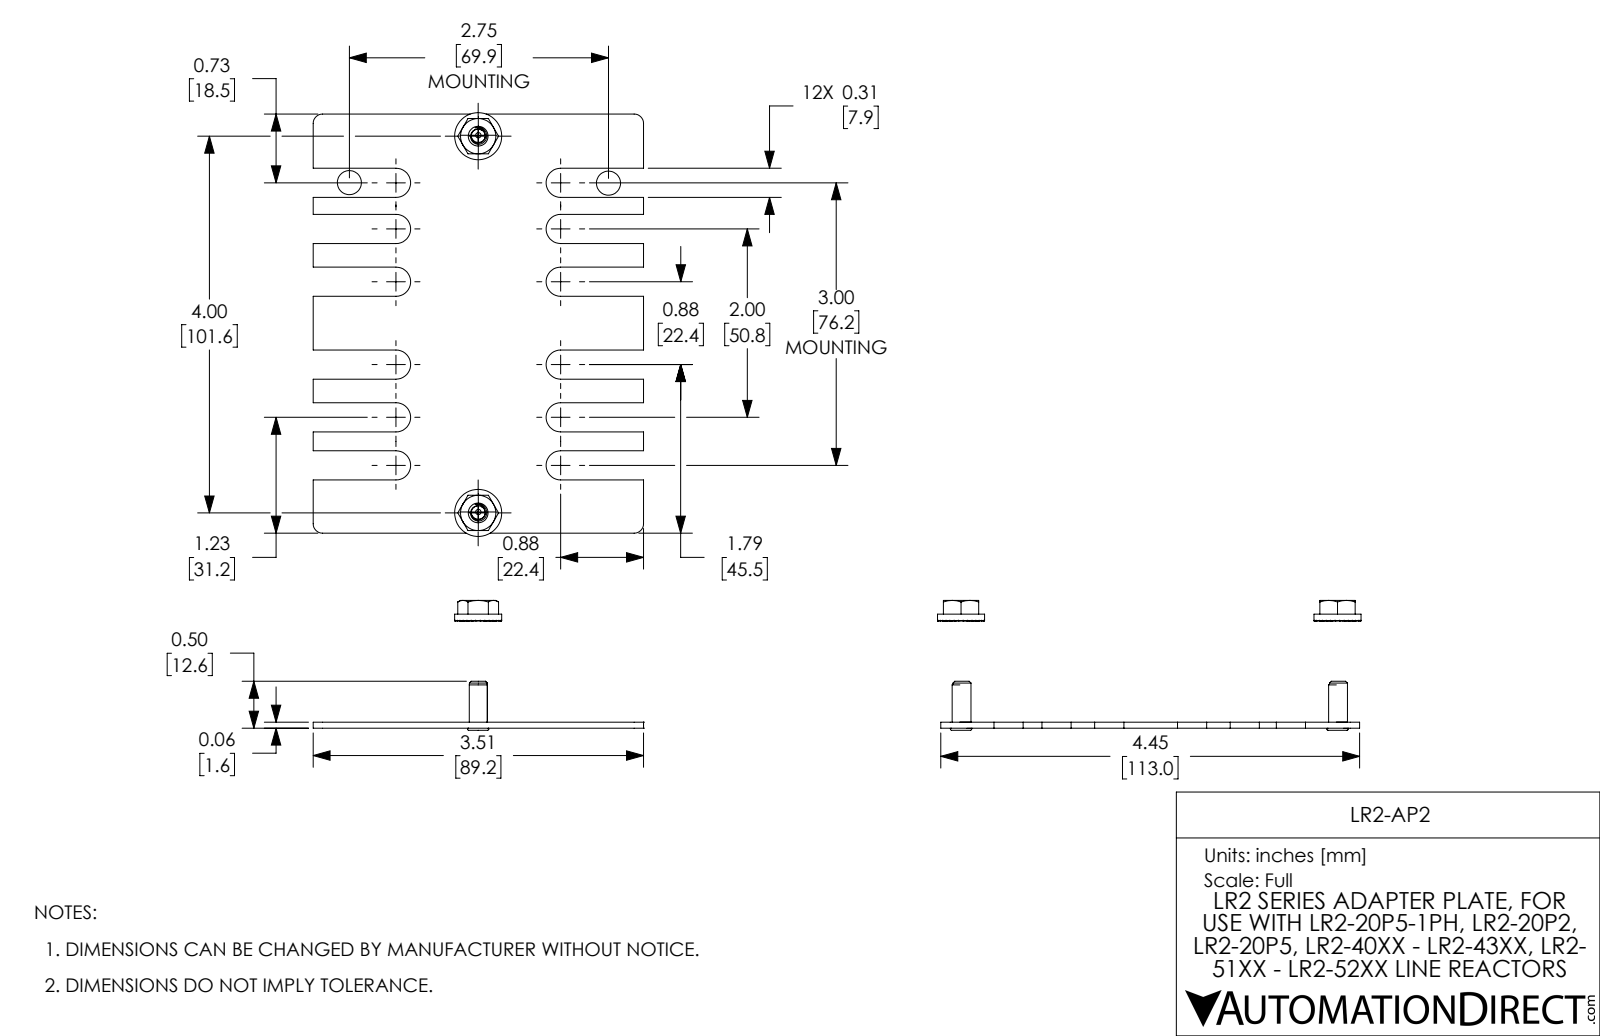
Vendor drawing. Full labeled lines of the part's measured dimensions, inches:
Part name (STEP PRODUCT): LR2-AP2 r1
STEP written by: SolidWorks 2017 (AUTOMOTIVE_DESIGN)
Units: inches
Bodies: 7 solids, 401 faces (200 planar, 100 cylindrical, 101 other)
Overall size (bounding box): 4.5 × 3.51 × 1.379
Volume: 0.861 in³ · Surface area: 29.37 in²
Round holes (diameter × count): ⌀0.149 ×2, ⌀0.189 ×2, ⌀0.19 ×2
Round bosses / shafts (diameter × count): ⌀0.19 ×3, ⌀0.5 ×2, ⌀0.37 ×2
Partial cylindrical surfaces — rounded edges, fillets, slot ends (radius × count): R0.155 ×12, R0.1 ×4
Main face-to-face distances: 0.063, 0.31, 2, 1.44, 0.56, 1.75, 0.25, 2.51, 0.51, 1.95
Hole centre spacings: 4, 3.99, 4.01
